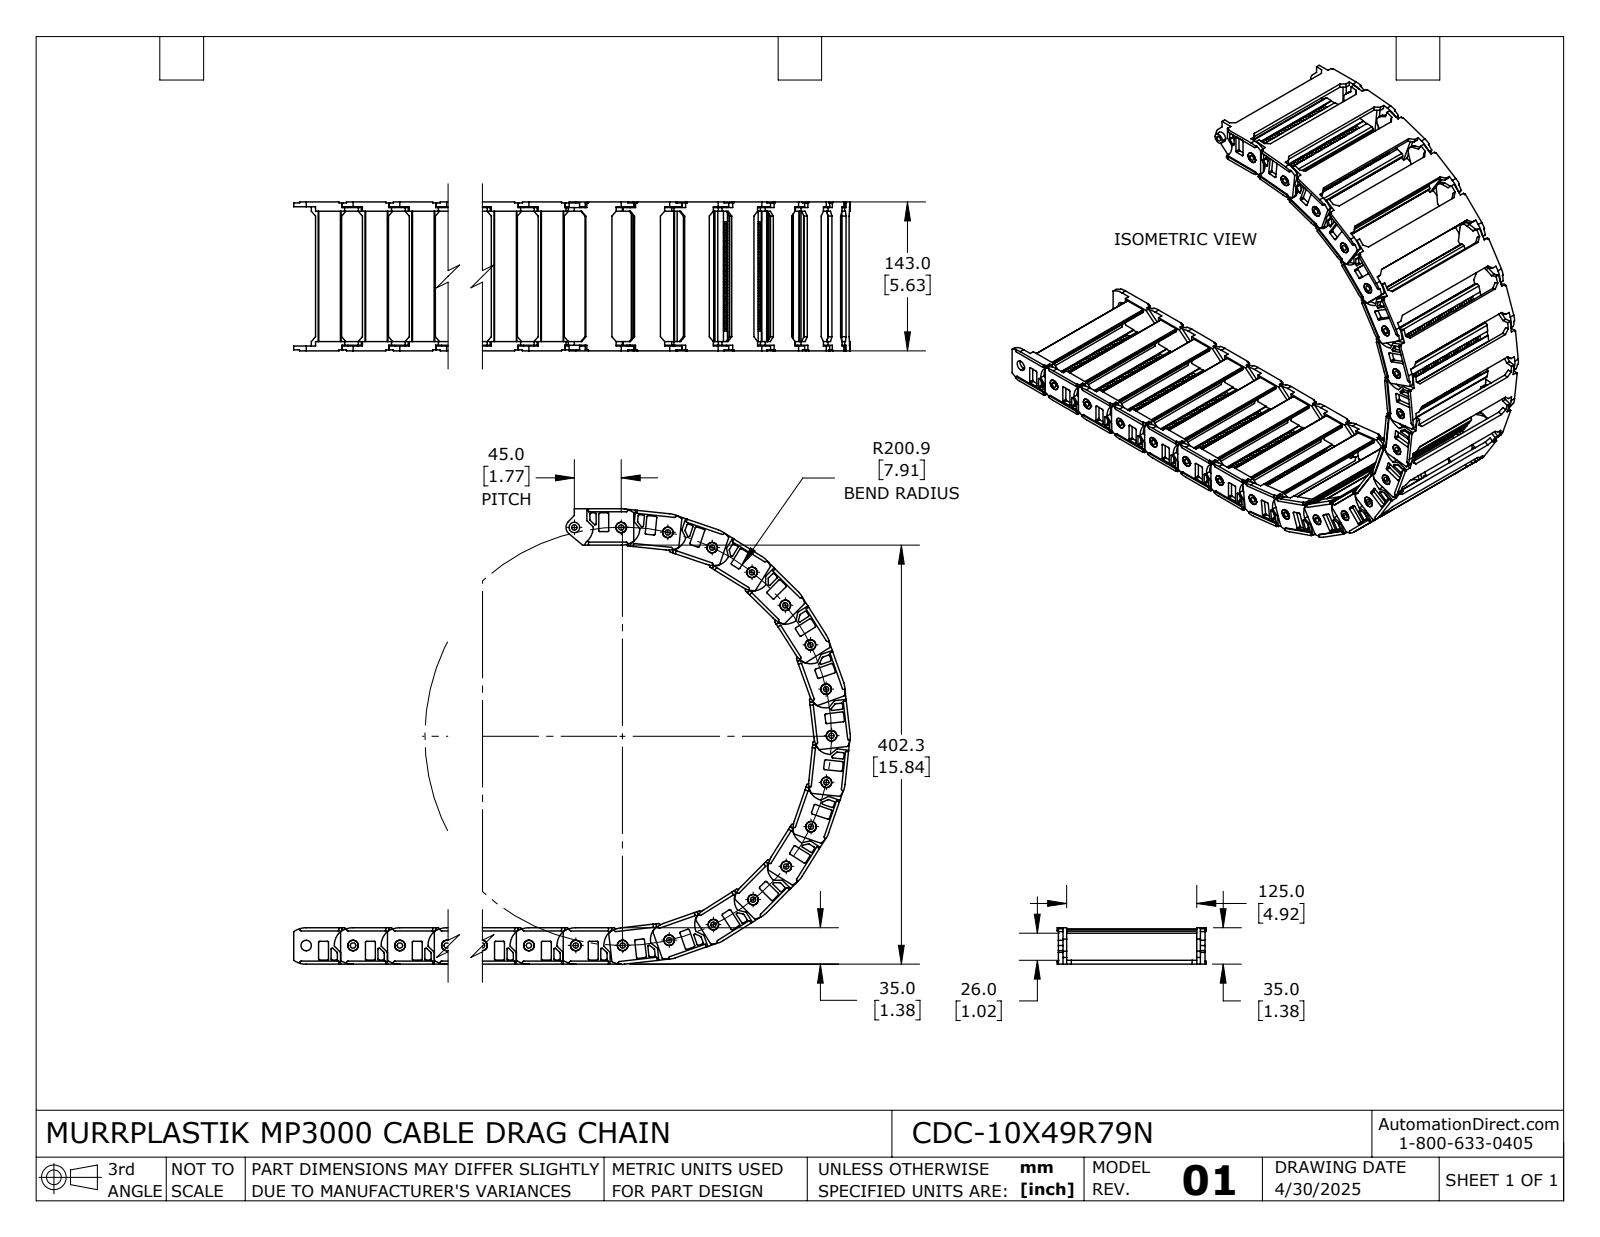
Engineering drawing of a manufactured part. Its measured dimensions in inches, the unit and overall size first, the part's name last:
Units: inches
Overall size (bounding box): 21.483 × 17.216 × 5.63
Round holes (diameter × count): ⌀0.201 ×22, ⌀0.398 ×22
Round bosses / shafts (diameter × count): ⌀0.394 ×22
Partial cylindrical surfaces — rounded edges, fillets, slot ends (radius × count): R0.039 ×176, R0.02 ×88, R0.059 ×44, R0.079 ×44, R0.827 ×44, R0.11 ×22, R0.315 ×22, R0.709 ×22
Main face-to-face distances: 0.157, 5.236, 0.315, 1.181, 1.331, 0.15, 0.146, 5.406, 0.169, 5.091
Hole centre spacings: 6.867, 1.772, 1.772, 3.522, 5.229, 6.869, 8.42, 5.228
Volume: 55.72 in³ · Surface area: 889.1 in²
Bodies: 22 solids, 6160 faces (5060 planar, 1100 cylindrical, 0 other)
Part name (STEP PRODUCT): CDC-10X49R79N
STEP written by: SolidWorks 2024 (AUTOMOTIVE_DESIGN)
